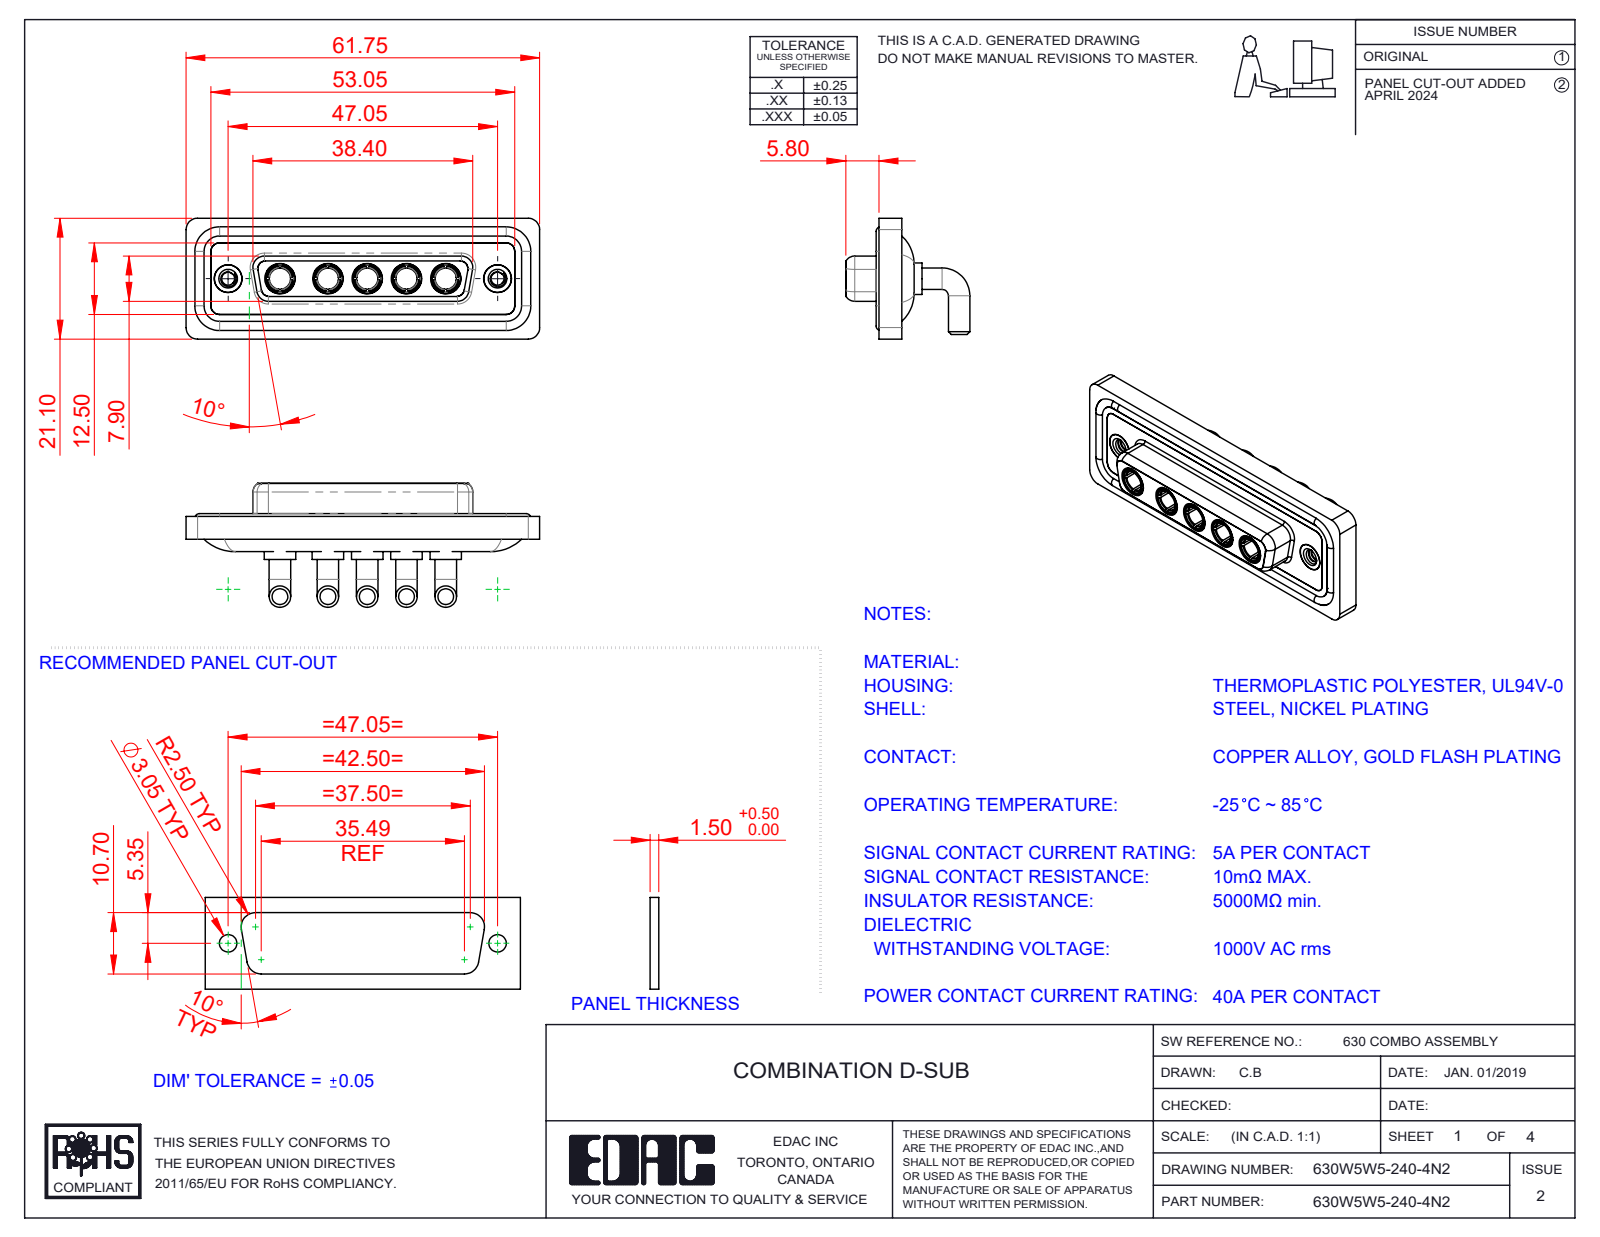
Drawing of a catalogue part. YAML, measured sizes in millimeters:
part_name: "630Combo Shell Rear_25 Contacts; 630Combo Shell Front_25 Contacts; 630Combo Threaded Rivet_2; Power Socket_40A RA (+3 more)"
step_written_by: "SolidWorks 2023 (CONFIG_CONTROL_DESIGN)"
units: millimeters
bodies: {solids: 17, faces: 776, planar: 250, cylindrical: 313, other: 213}
overall_size: [61.75, 21.68, 21.1]
volume: 8799
surface_area: 14032
round_holes:
  - {diameter: 4.85, count: 7}
  - {diameter: 3.7, count: 5}
  - {diameter: 5.3, count: 5}
  - {diameter: 2.26, count: 2}
  - {diameter: 4, count: 2}
  - {diameter: 4.05, count: 2}
  - {diameter: 5, count: 2}
round_bosses_or_shafts:
  - {diameter: 3.75, count: 10}
  - {diameter: 5.5, count: 5}
  - {diameter: 5.2, count: 5}
  - {diameter: 4.96, count: 5}
  - {diameter: 4.75, count: 5}
  - {diameter: 1.6, count: 4}
  - {diameter: 4.95, count: 2}
  - {diameter: 4.8, count: 2}
partial_cylinders:
  - {radius: 1.5, count: 18}
  - {radius: 2, count: 18}
  - {radius: 1.35, count: 8}
  - {radius: 1.6, count: 8}
  - {radius: 2.1, count: 5}
  - {radius: 0.25, count: 4}
  - {radius: 0.5, count: 4}
  - {radius: 0.6, count: 4}
face_to_face_distances: [0.4, 1.8, 4.1, 1.1, 2.5, 3.1, 3.7, 1.6, 1.5, 2.9]
hole_center_spacings: [6.86, 9.04, 38.01, 6.87, 8.38, 13.72, 13.73, 15.25]
